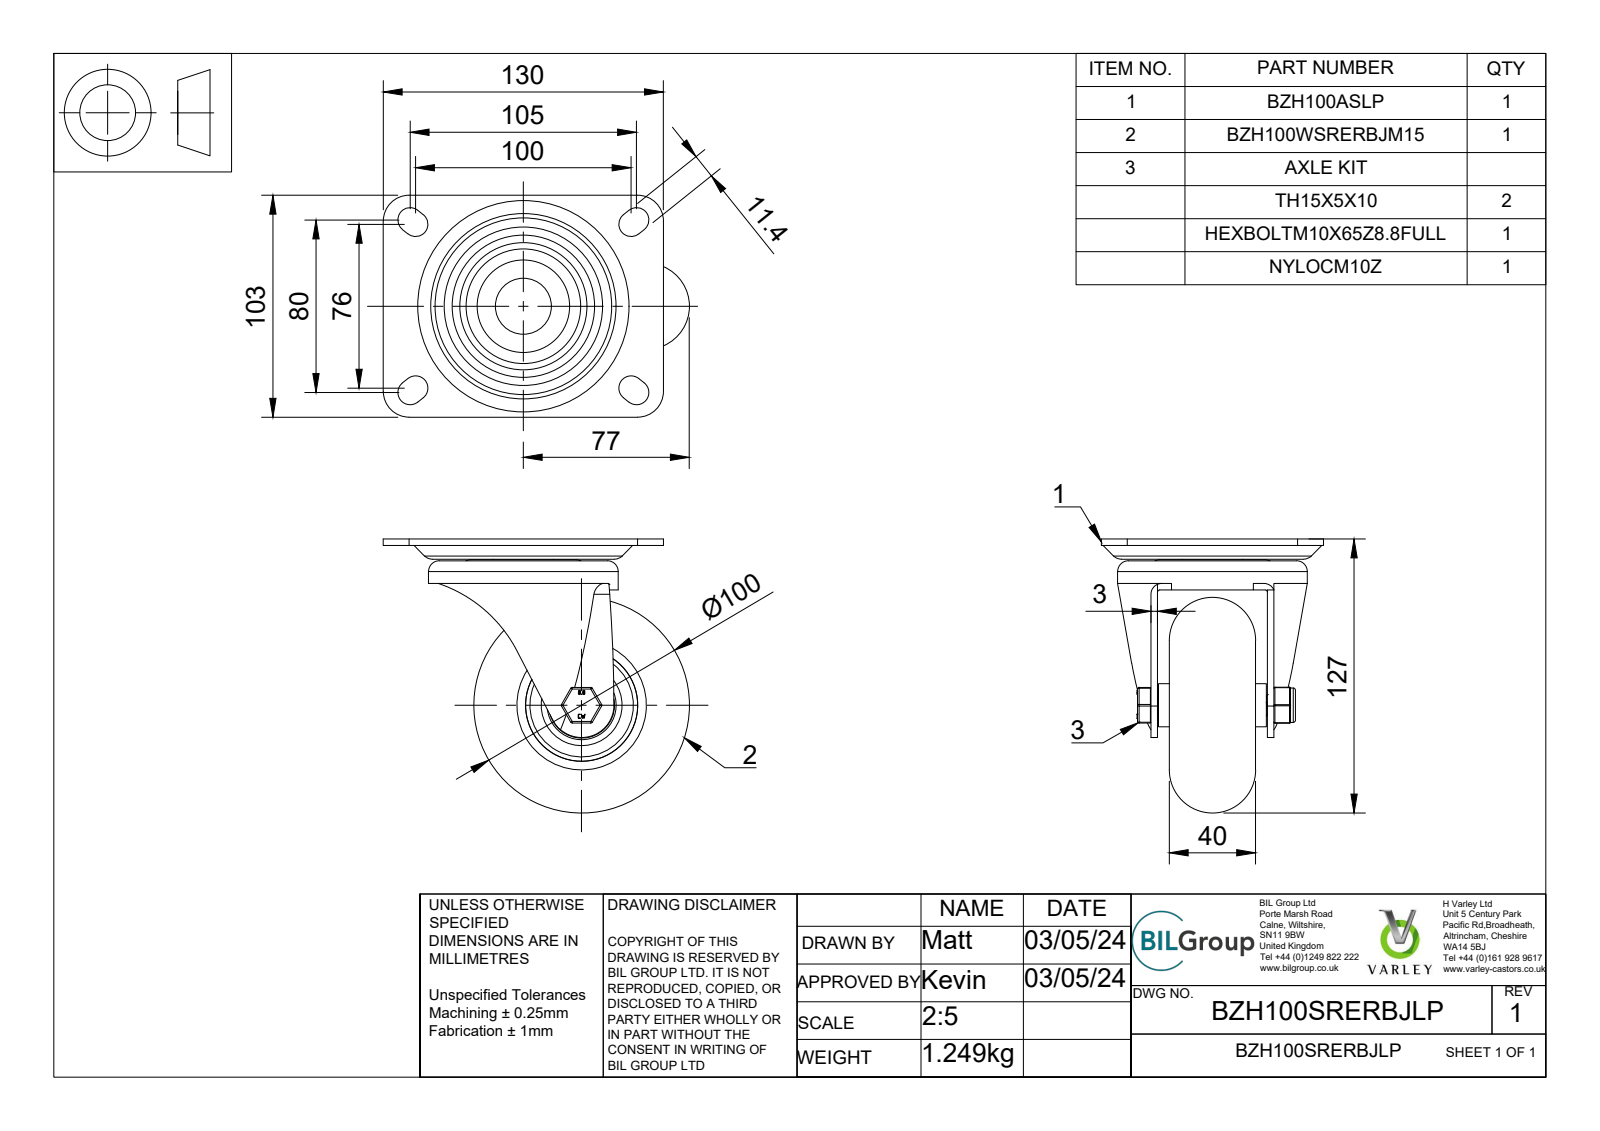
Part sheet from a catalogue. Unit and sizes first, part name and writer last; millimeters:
Units: millimetres
Overall size (bounding box): 142 × 127.13 × 103
Round holes (diameter × count): ⌀10 ×1, ⌀10.5 ×1, ⌀12 ×1, ⌀15 ×1, ⌀20.5 ×1, ⌀26 ×1, ⌀26.8 ×1, ⌀28 ×1, ⌀28.2 ×1, ⌀30 ×1, ⌀32 ×1, ⌀48 ×1
Round bosses / shafts (diameter × count): ⌀88 ×1, ⌀37.5 ×1, ⌀36 ×1, ⌀28 ×1, ⌀26 ×1, ⌀21.5 ×1, ⌀20 ×1, ⌀19 ×1
Partial cylindrical surfaces — rounded edges, fillets, slot ends (radius × count): R0.5 ×18, R0.75 ×12, R5.7 ×8, R12 ×4, R1 ×2, R5 ×2, R11.4 ×1, R12.9 ×1
Main face-to-face distances: 3, 14.5, 39.5, 8.5, 3.5, 48.5, 54, 5.5, 45.5, 0.5
Volume: 347 332 mm³ · Surface area: 127 884 mm²
Bodies: 38 solids, 1126 faces (368 planar, 238 cylindrical, 520 other)
Part name (STEP PRODUCT): BZH100SRERBJLP v3; BZH100ASLP v1; ZINC PLATED PRESSED STEEL FORK; ZINC PLATED PRESSED STEEL TOP PLATE (+8 more)
STEP written by: Autodesk Translation Framework v12.20.1.177 (AUTOMOTIVE_DESIGN)
